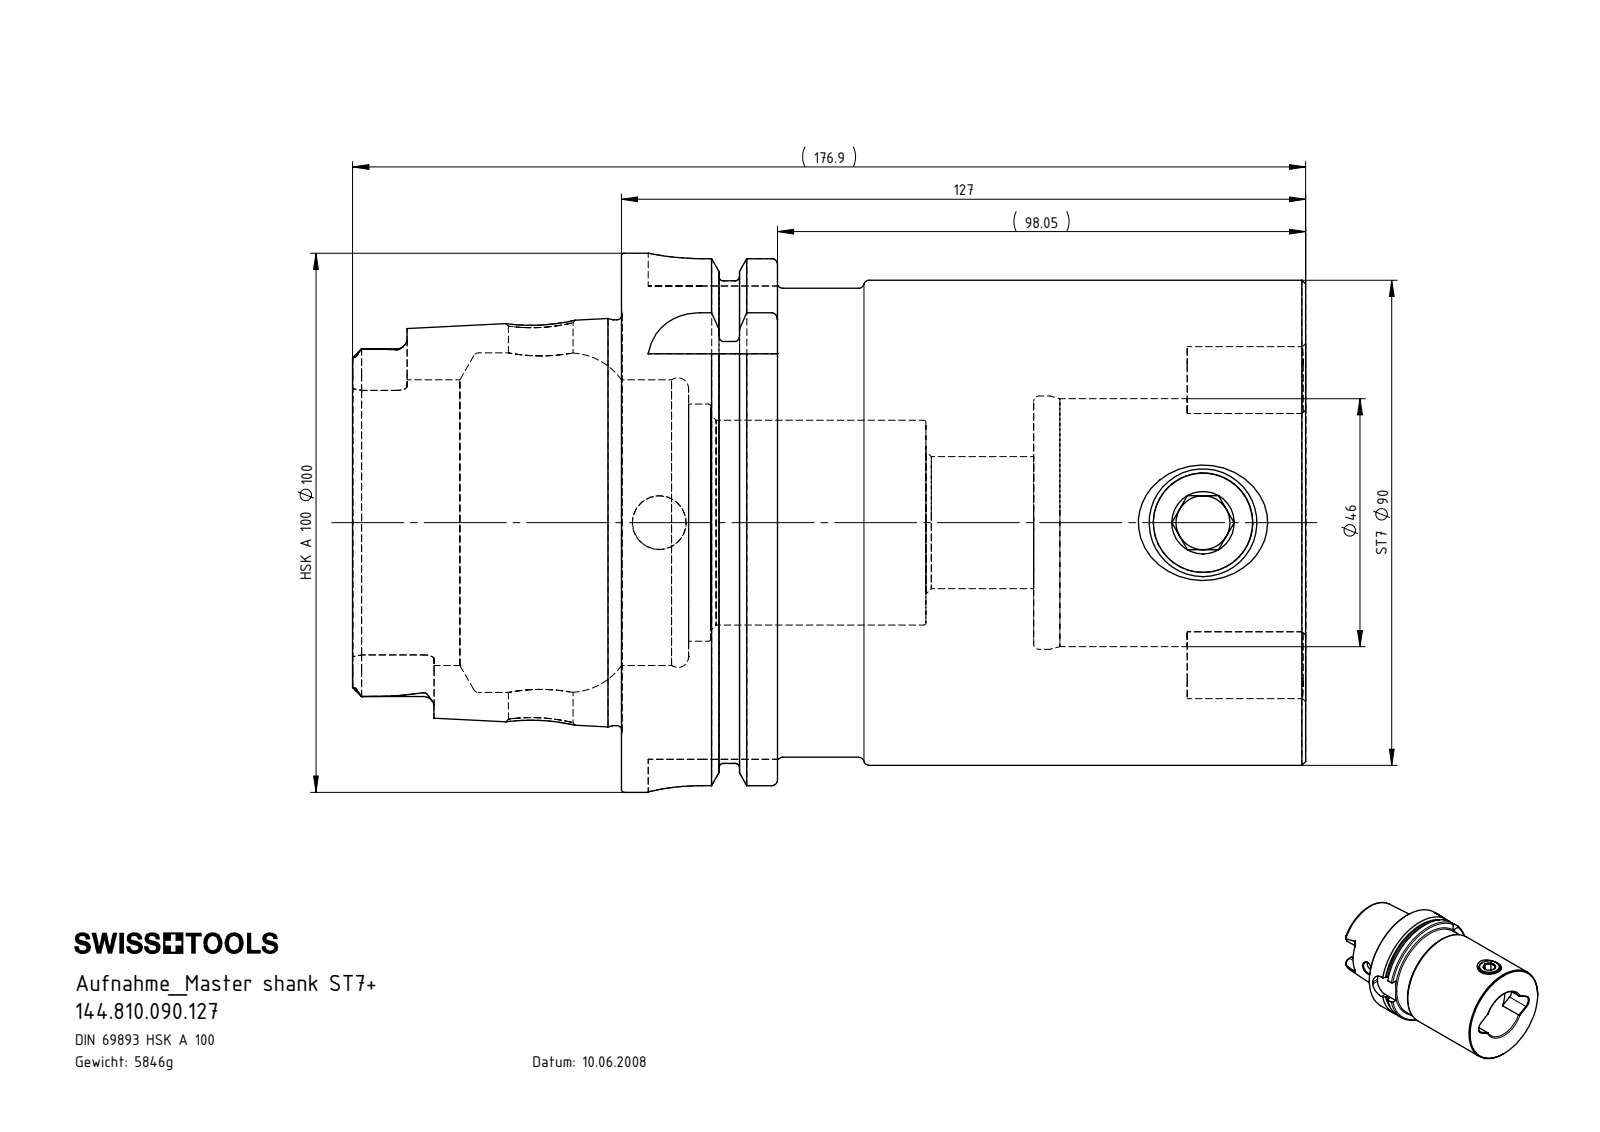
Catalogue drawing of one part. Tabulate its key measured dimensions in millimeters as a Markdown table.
| quantity | value |
| --- | --- |
| part name | ST7-ER4.002.020_A; HA0-ST7.K01.127; HA0-ST7.K01.127_A_Fertigbearbeitung; ST7-ER1.001.029_A |
| STEP written by | SolidWorks 2015 (CONFIG_CONTROL_DESIGN) |
| units | millimeters |
| bodies | 3 solids, 253 faces (70 planar, 71 cylindrical, 112 other) |
| overall size | 176.9 × 100 × 100 |
| volume | 745 134 mm³ |
| surface area | 99 844 mm² |
| round holes (diameter × count) | 12 × 2, 10 × 1, 18.5 × 1, 22.5 × 1, 24.5 × 1, 24.6 × 1, 38 × 1, 44 × 1, 46 × 1, 47 × 1, 53 × 1, 63 × 1 |
| round bosses / shafts (diameter × count) | 100 × 1, 91.95 × 1, 90 × 1, 87 × 1, 75.26 × 1, 43.5 × 1, 40 × 1, 37 × 1 |
| partial cylindrical surfaces (radius × count) | 1.9 × 6, 4.88 × 4, 10 × 4, 6.5 × 2 |
| main face-to-face distances | 127, 20, 43.95, 76.5, 50.5, 28.95, 47.55, 98.05, 12.55, 32.55 |
| hole center spacings | 100.95 |
